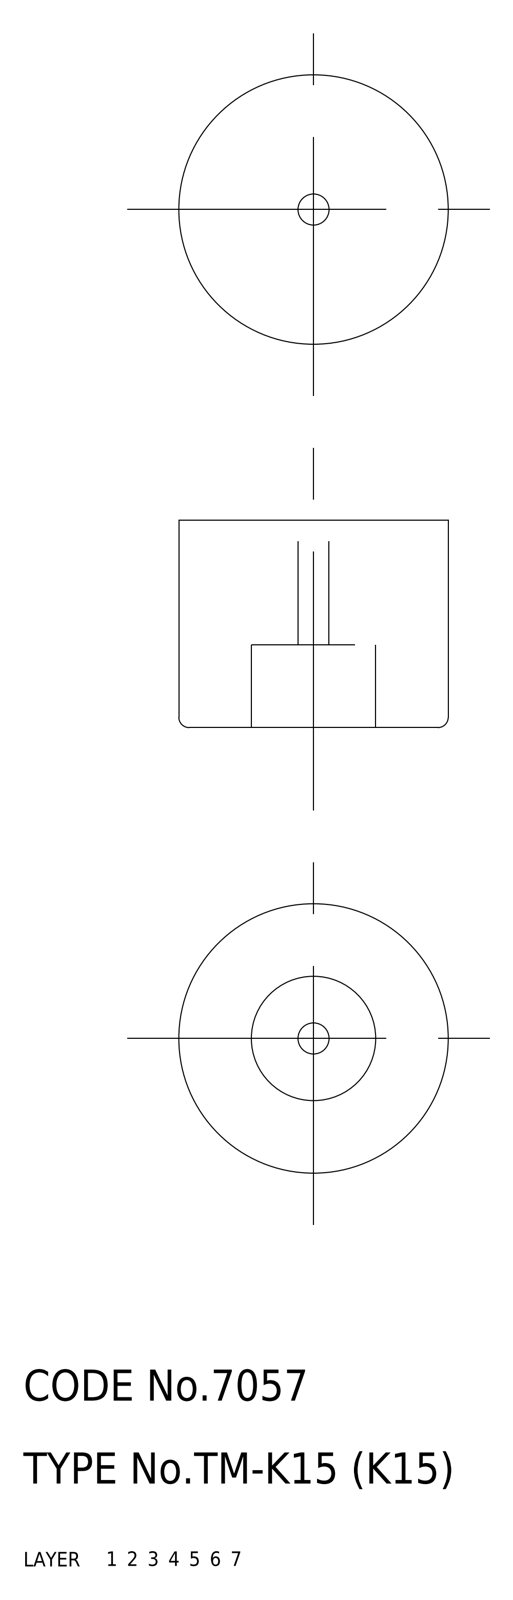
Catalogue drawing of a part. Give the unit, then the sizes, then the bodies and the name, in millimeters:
Units: millimetres
Overall size (bounding box): 26 × 26 × 20
Volume: 9 633 mm³ · Surface area: 3 062 mm²
Bodies: 1 solid, 11 faces (0 planar, 0 cylindrical, 11 other)
Part name (STEP PRODUCT): rubber foot
STEP written by: CADfix (AUTOMOTIVE_DESIGN)
